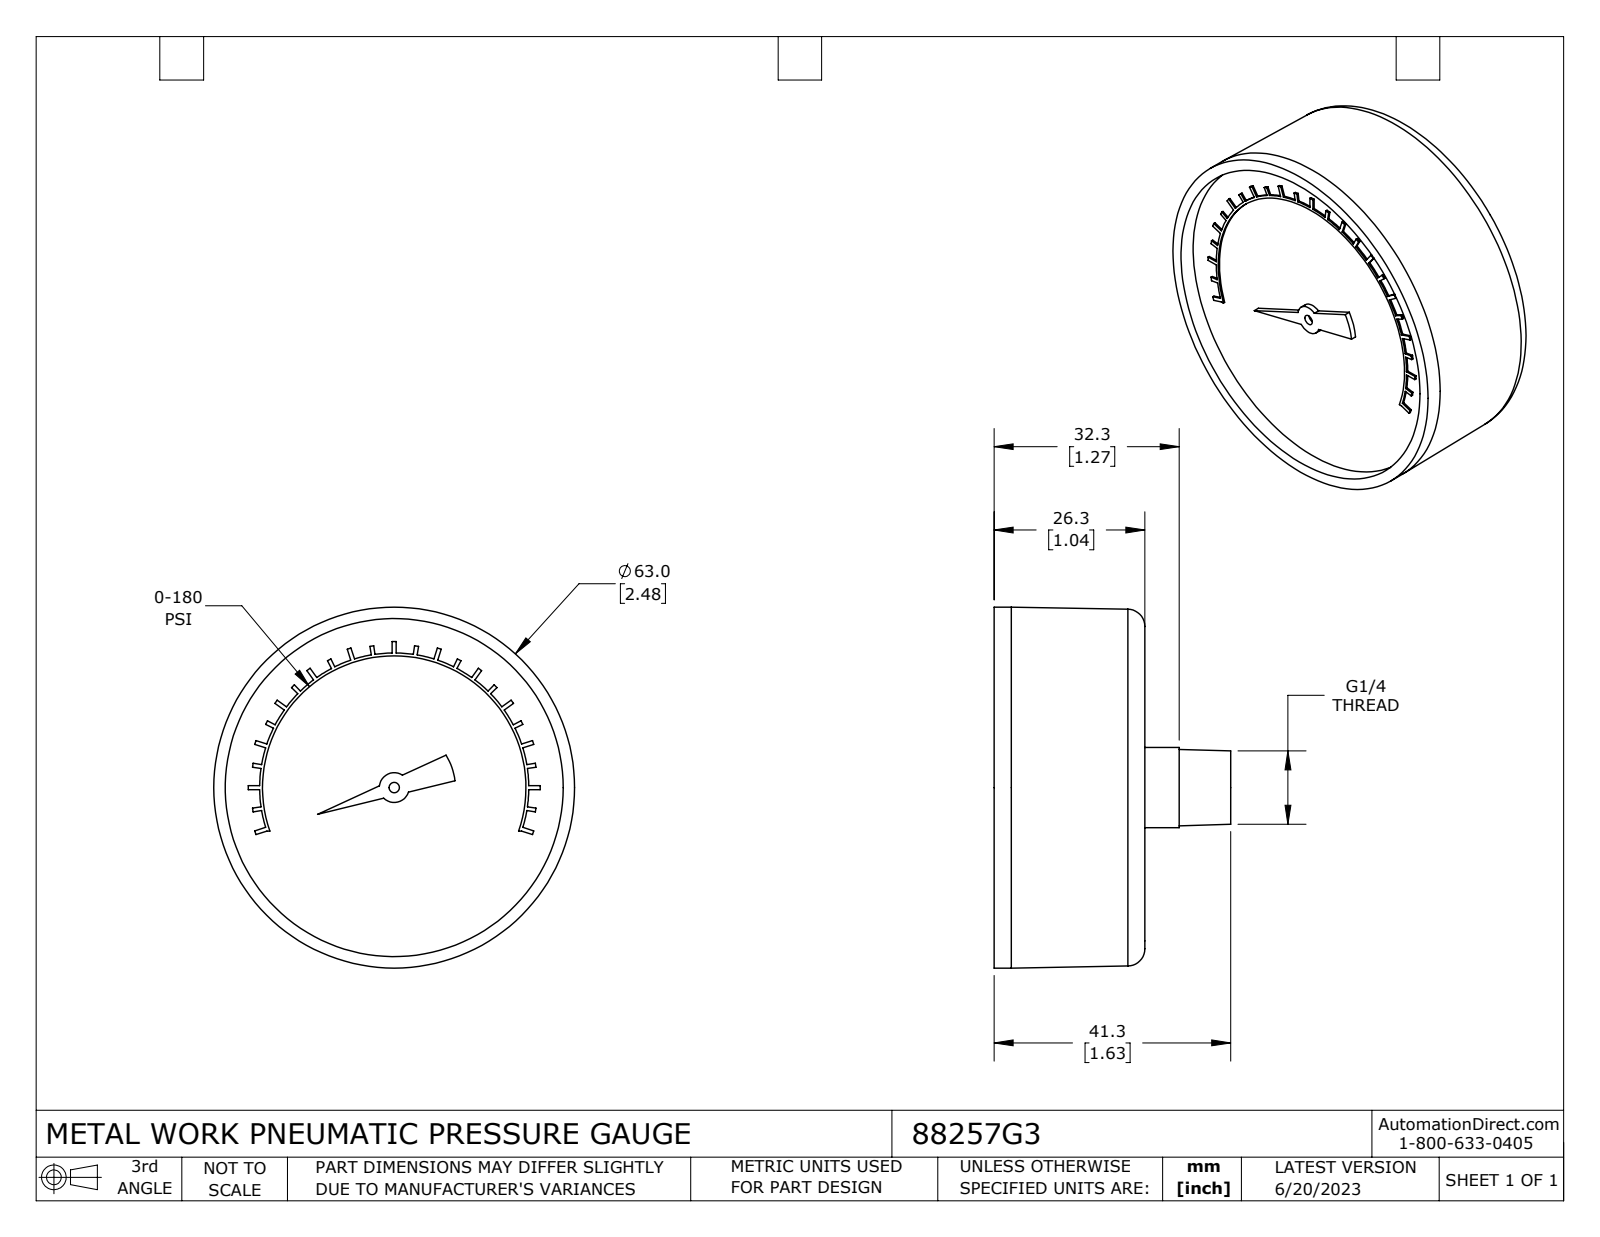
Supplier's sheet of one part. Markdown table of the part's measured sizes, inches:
| quantity | value |
| --- | --- |
| part name | 88257G3 |
| STEP written by | SolidWorks 2021 (CONFIG_CONTROL_DESIGN) |
| units | inches |
| bodies | 1 solid, 135 faces (93 planar, 36 cylindrical, 6 other) |
| overall size | 2.48 × 2.48 × 1.626 |
| volume | 4.633 in³ |
| surface area | 19.54 in² |
| round holes (diameter × count) | 0.071 × 1, 2.323 × 1 |
| round bosses / shafts (diameter × count) | 2.48 × 1 |
| partial cylindrical surfaces (radius × count) | 0.103 × 1, 0.42 × 1, 0.895 × 1, 0.902 × 1, 0.903 × 1, 0.905 × 1, 0.906 × 1, 0.908 × 1 |
| main face-to-face distances | 0.917, 1.035, 0.118, 0.551, 0.591, 1.508, 1.626, 1.52, 0.929, 0.106 |
